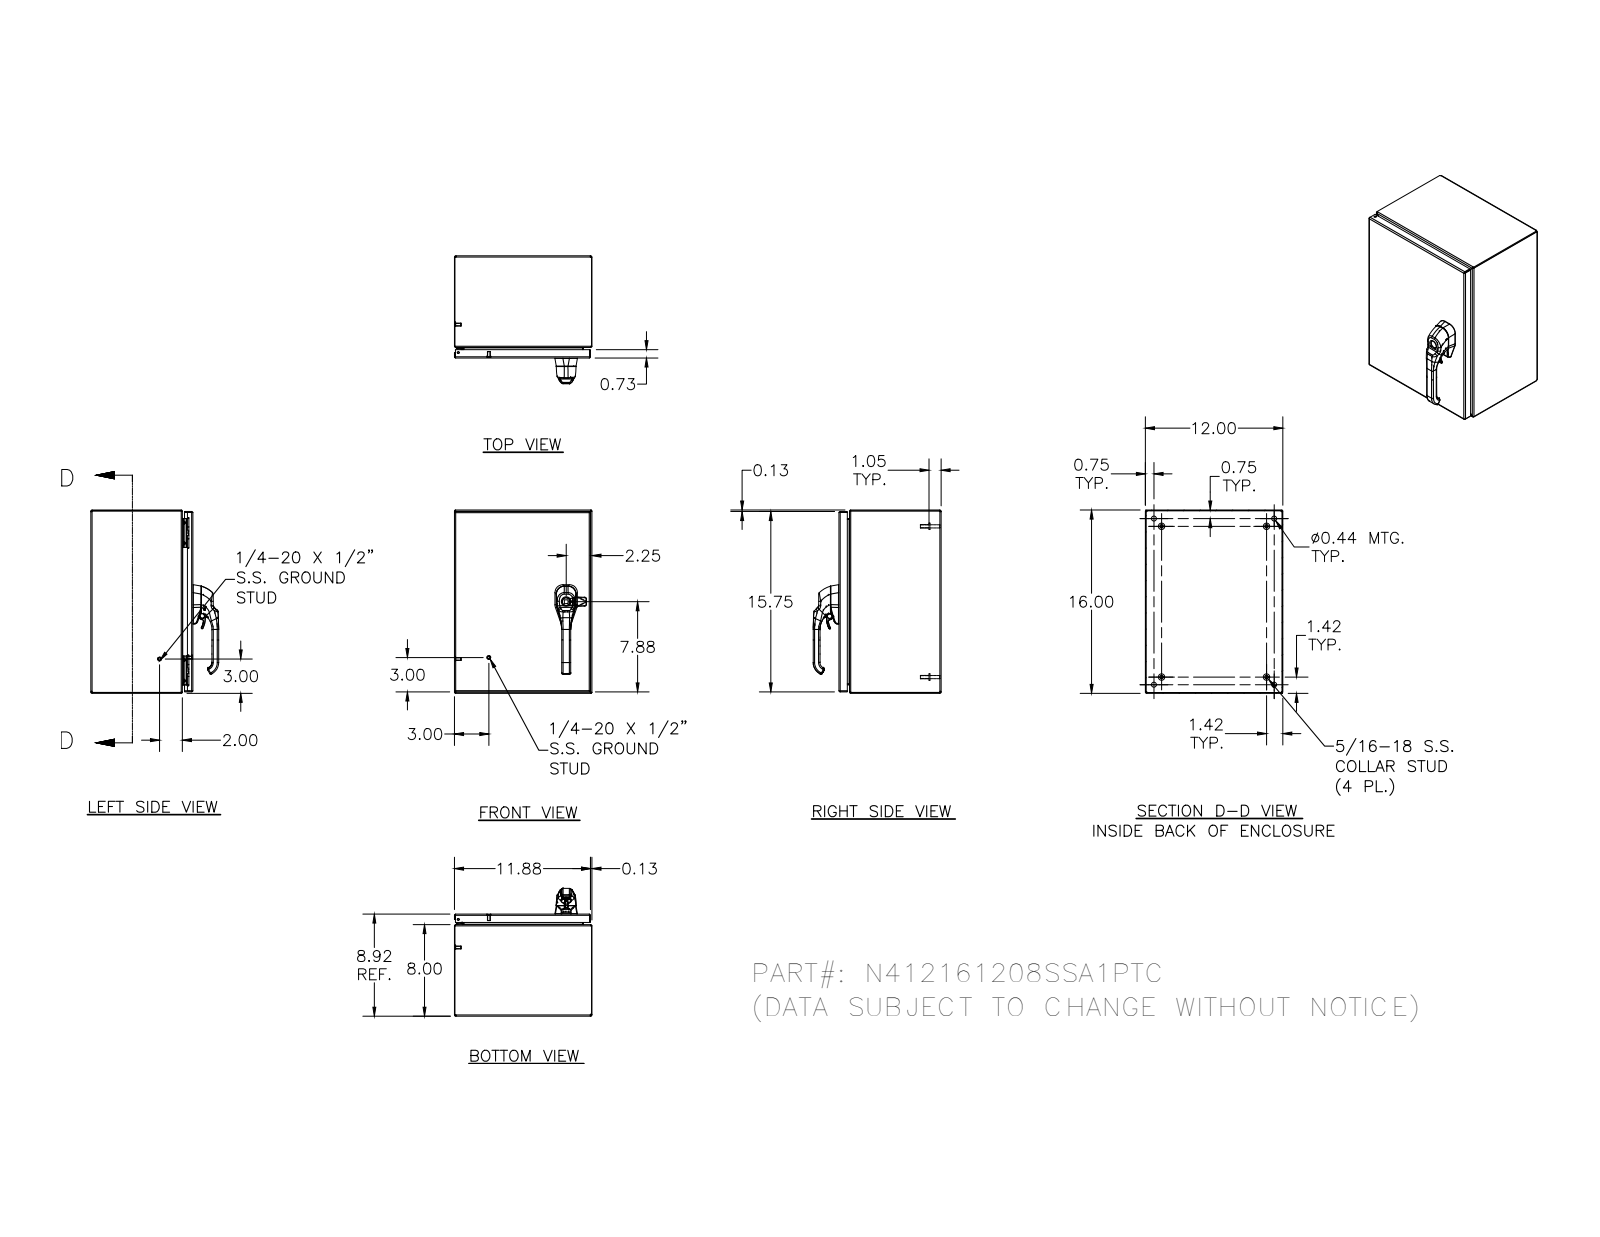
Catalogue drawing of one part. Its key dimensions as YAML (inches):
part_name: "N412161208SSA1PTC; N412161208SSA1PTCBKP; N4121612SSA1PTCLID; HFW328176 (+8 more)"
step_written_by: "Autodesk Inventor 2012 (AUTOMOTIVE_DESIGN)"
units: inches
bodies: {solids: 41, faces: 2784, planar: 882, cylindrical: 1037, other: 865}
overall_size: [16, 12, 11.166]
volume: 77.43
surface_area: 2009
round_holes:
  - {diameter: 0.188, count: 5}
  - {diameter: 0.093, count: 4}
  - {diameter: 0.152, count: 4}
  - {diameter: 0.167, count: 4}
  - {diameter: 0.172, count: 4}
  - {diameter: 0.437, count: 4}
  - {diameter: 0.213, count: 3}
  - {diameter: 0.281, count: 3}
  - {diameter: 0.156, count: 2}
  - {diameter: 0.315, count: 2}
  - {diameter: 0.402, count: 2}
  - {diameter: 0.413, count: 2}
round_bosses_or_shafts:
  - {diameter: 0.25, count: 10}
  - {diameter: 0.563, count: 4}
  - {diameter: 0.36, count: 4}
  - {diameter: 0.32, count: 4}
  - {diameter: 0.3, count: 4}
  - {diameter: 0.275, count: 4}
  - {diameter: 0.256, count: 4}
  - {diameter: 0.164, count: 4}
partial_cylinders:
  - {radius: 0.02, count: 173}
  - {radius: 0.012, count: 101}
  - {radius: 0.031, count: 30}
  - {radius: 0.05, count: 26}
  - {radius: 0.019, count: 21}
  - {radius: 0.105, count: 20}
  - {radius: 0.016, count: 18}
  - {radius: 0.079, count: 14}
face_to_face_distances: [0.074, 8.843, 11.926, 15.926, 8.917, 8.769, 11.852, 12, 16, 15.852]
hole_center_spacings: [11.996, 0.017, 0.66, 12.656, 0.019, 0.5, 0.648, 0.656]
